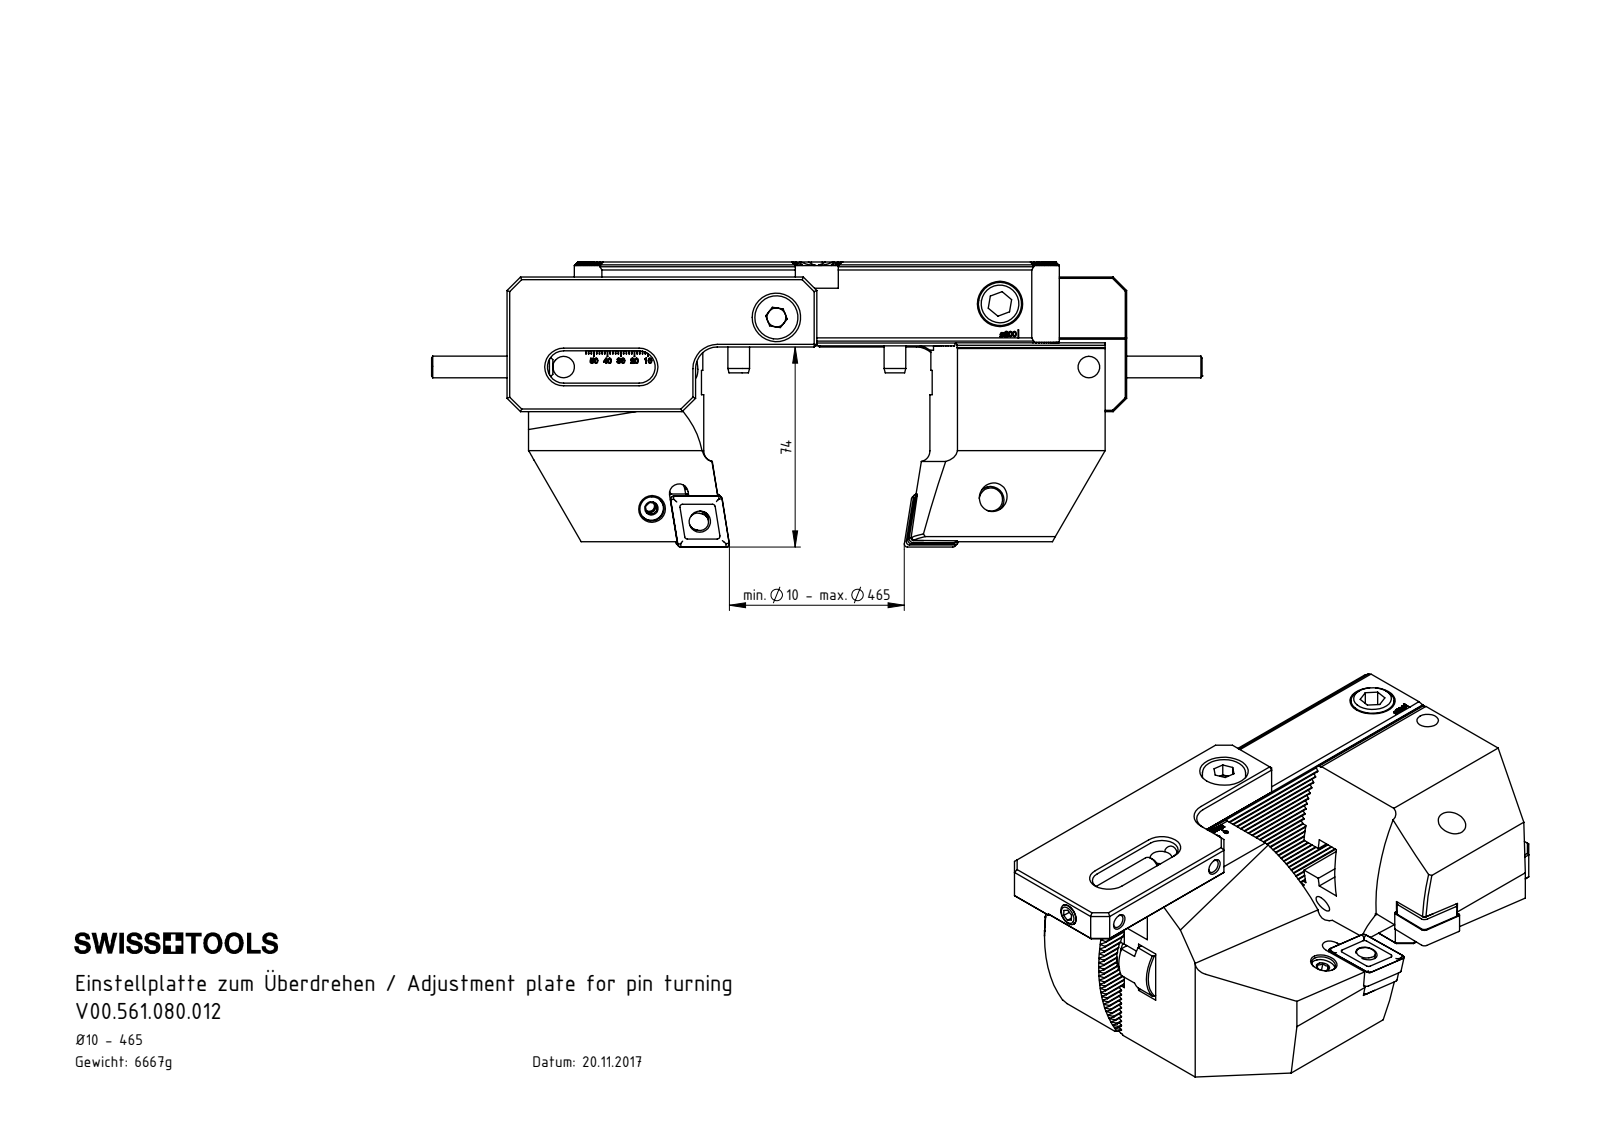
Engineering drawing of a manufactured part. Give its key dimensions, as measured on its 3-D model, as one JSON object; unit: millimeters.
{"part_name": "ISO 4026 - M8 x 45; DIN 7984 - M10 x 16; V00.561.080.012; VK1-ER7.002.012_C (+1 more)", "step_written_by": "SolidWorks 2022 (AUTOMOTIVE_DESIGN)", "units": "millimeters", "bodies": {"solids": 5, "faces": 139, "planar": 74, "cylindrical": 30, "other": 35}, "overall_size": [126.3, 50, 22], "volume_mm3": 50069, "surface_area_mm2": 17562, "round_holes": [[5, 2], [6, 2], [6.8, 1], [11, 1], [18, 1]], "round_bosses_or_shafts": [[16, 1], [10, 1], [8, 1]], "partial_cylinders_radius": [[6, 2], [8, 1]], "face_to_face_distances": [12, 0.5, 11.5, 50, 6, 26, 24, 5.5, 27.4, 39.4], "hole_center_spacings": [7.9, 18.55, 19.61, 50]}
